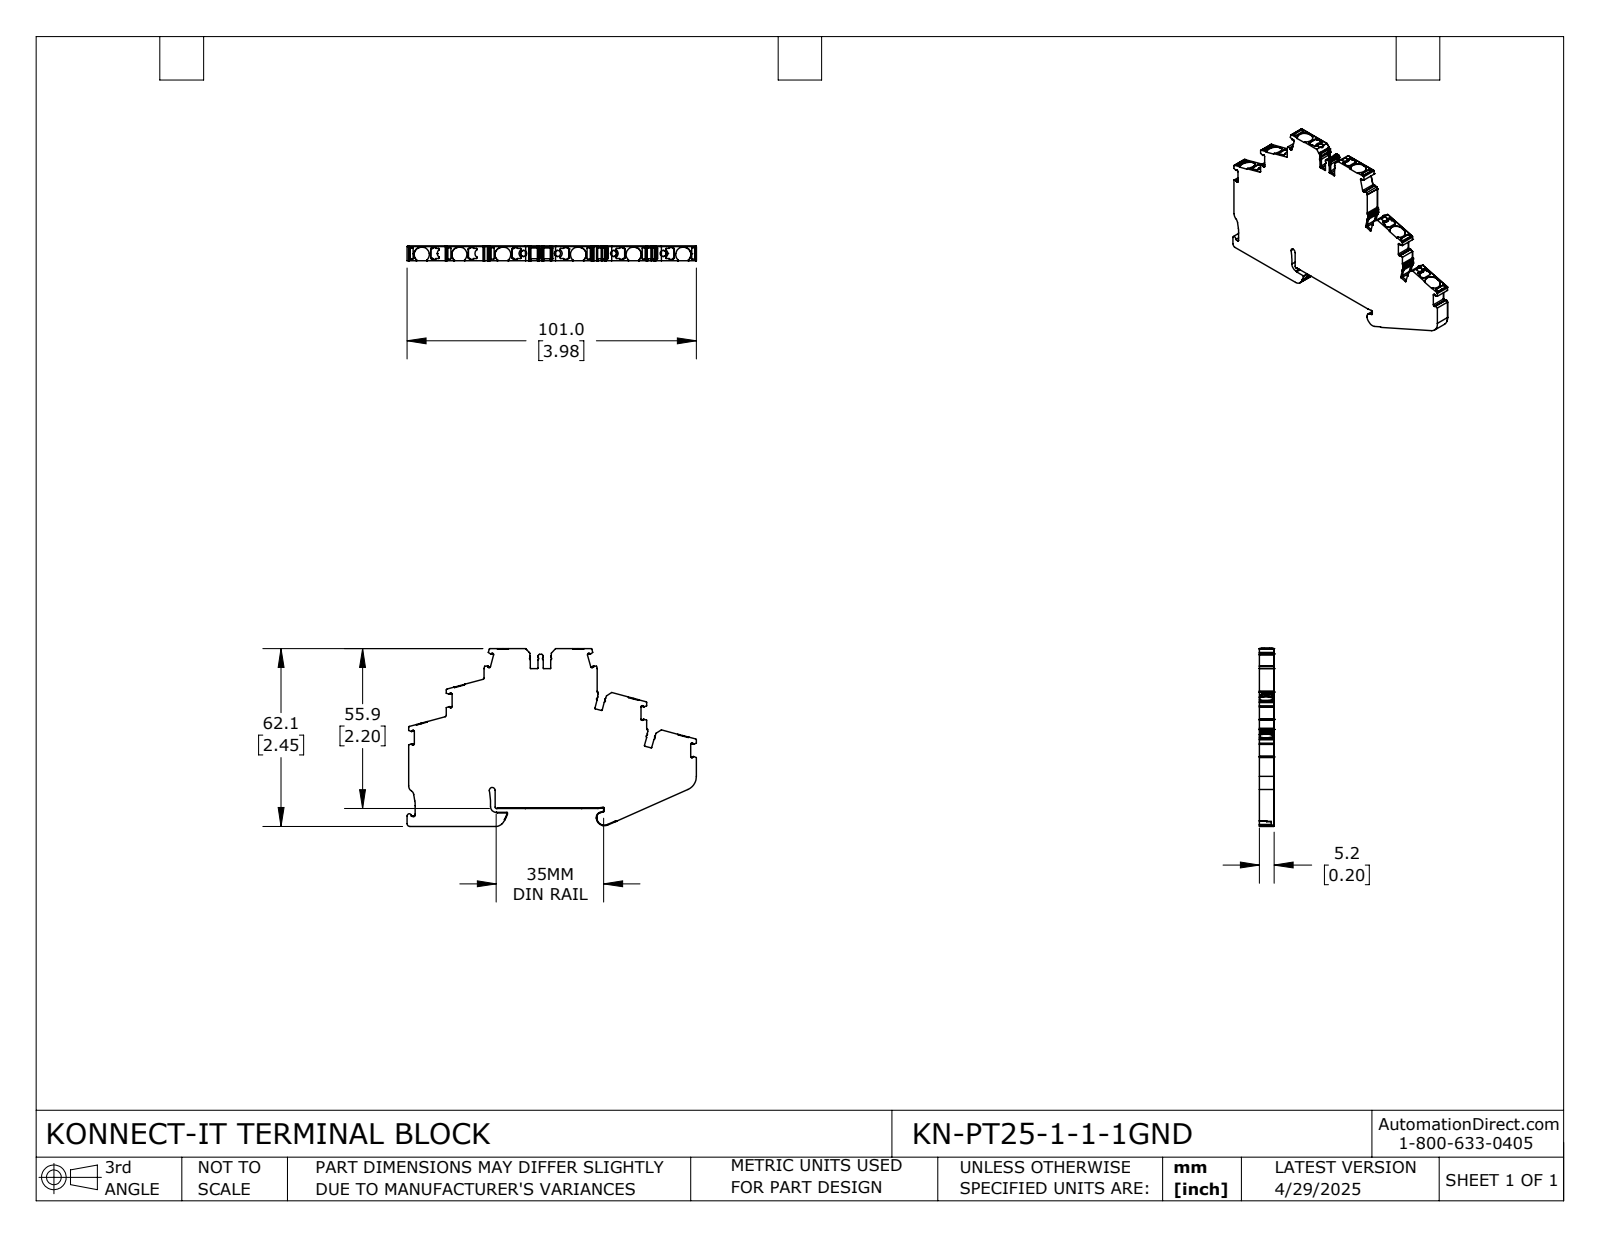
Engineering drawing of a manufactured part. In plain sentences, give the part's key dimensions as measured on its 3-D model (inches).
The part is named "KN-PT25-1-1-1GND". Its 3-D file was written by "SolidWorks 2024 (CONFIG_CONTROL_DESIGN)". It is 1 solid with 1010 faces: 514 planar, 483 cylindrical and 13 other. Overall it measures 3.977 by 2.445 by 0.203 inches. Its volume is 1.35 cubic inches and its surface area 16.8 square inches. Round holes: 4 of diameter 0.083. Partial cylindrical surfaces (rounded edges, fillets, slot ends): 119 of radius 0.008, 47 of radius 0.012, 37 of radius 0.004, 24 of radius 0.02, 23 of radius 0.016, 14 of radius 0.024, 12 of radius 0.006, 12 of radius 0.01. The main face-to-face distances are 0.203, 2.191, 0.246, 0.079, 2.437, 0.254, 2.183, 0.319, 0.682, 0.519. The hole center spacings are 0.466, 0.792.
